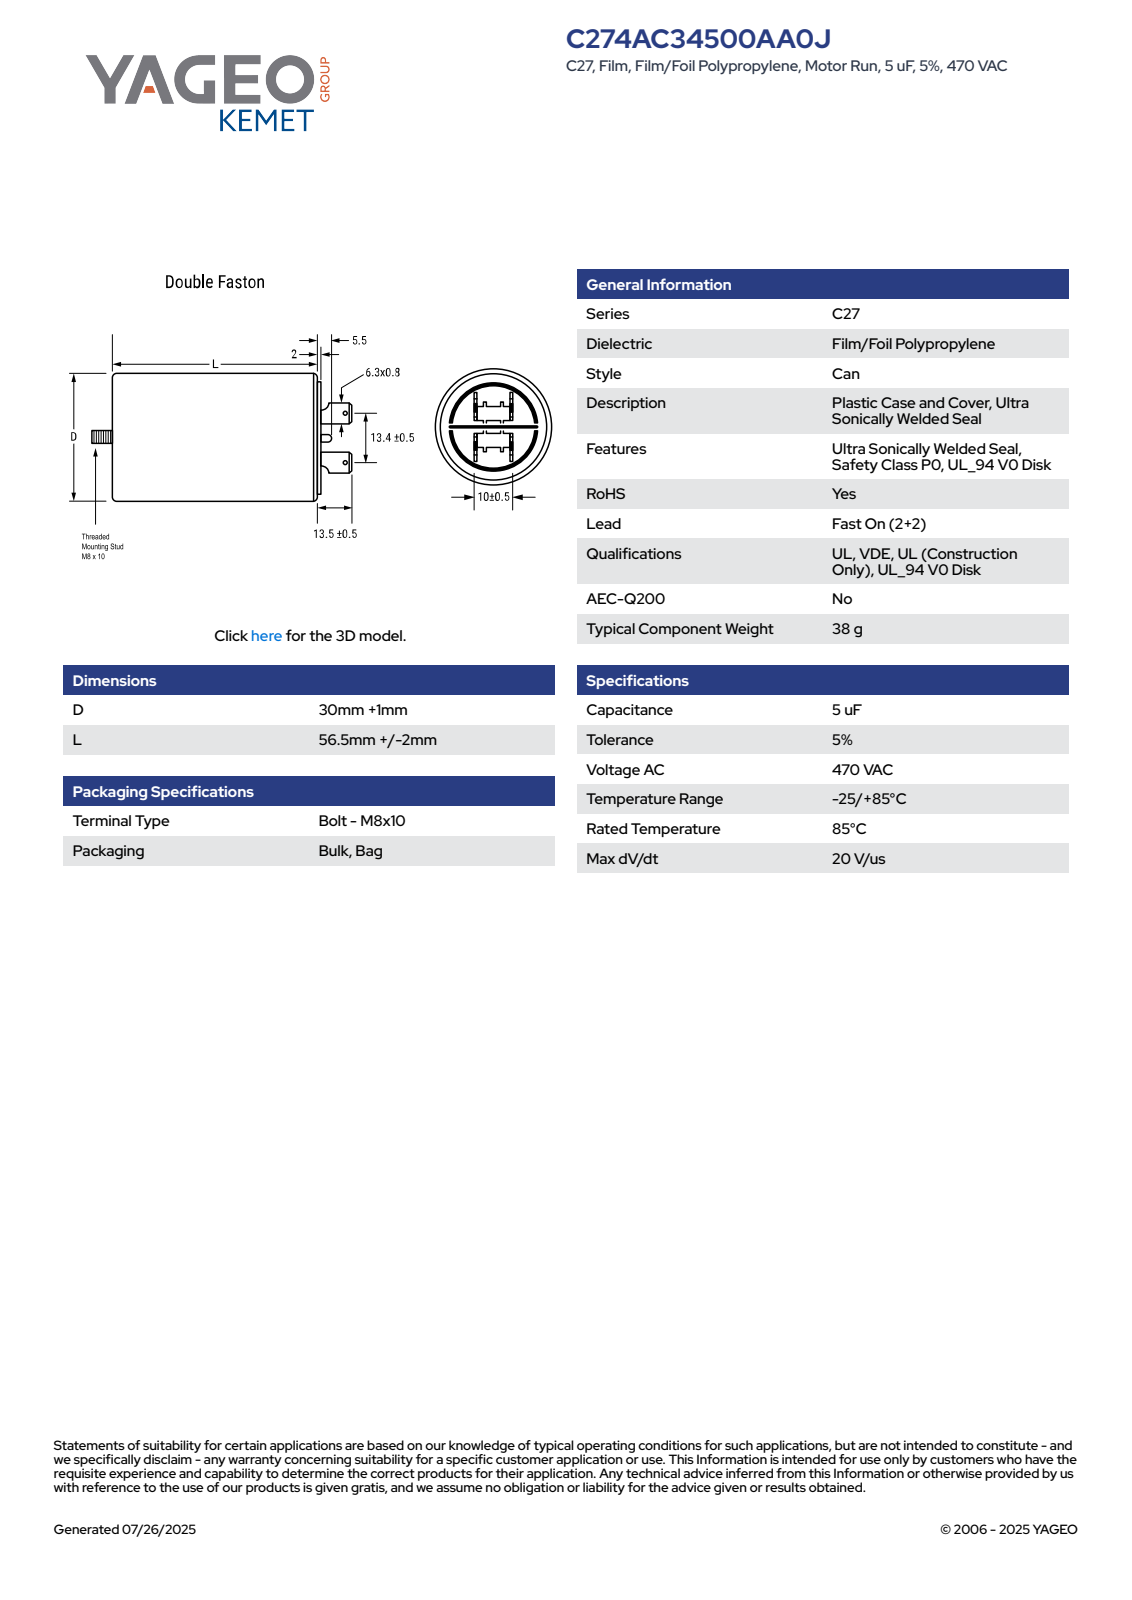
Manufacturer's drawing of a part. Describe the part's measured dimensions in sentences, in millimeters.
The part is named "CFM_C27DF_30X56.5_D31L58.5". Its 3-D file was written by "SolidWorks 2014 (AUTOMOTIVE_DESIGN)". It is 1 solid with 137 faces: 49 planar, 53 cylindrical and 35 other. Overall it measures 82.5 by 31 by 31 millimeters. Its volume is 45 652 cubic millimeters and its surface area 8 259 square millimeters. Round holes: 2 of diameter 1.2. Round bosses or shafts: 1 of diameter 31, 1 of diameter 23.85, 1 of diameter 8. Partial cylindrical surfaces (rounded edges, fillets, slot ends): 9 of radius 0.25, 2 of radius 4, 1 of radius 15.49. The main face-to-face distances are 60.5, 0.8, 9.7, 10.5, 8.9, 58.5, 2, 0.5, 10, 68.5. The hole center spacings are 13.9.
